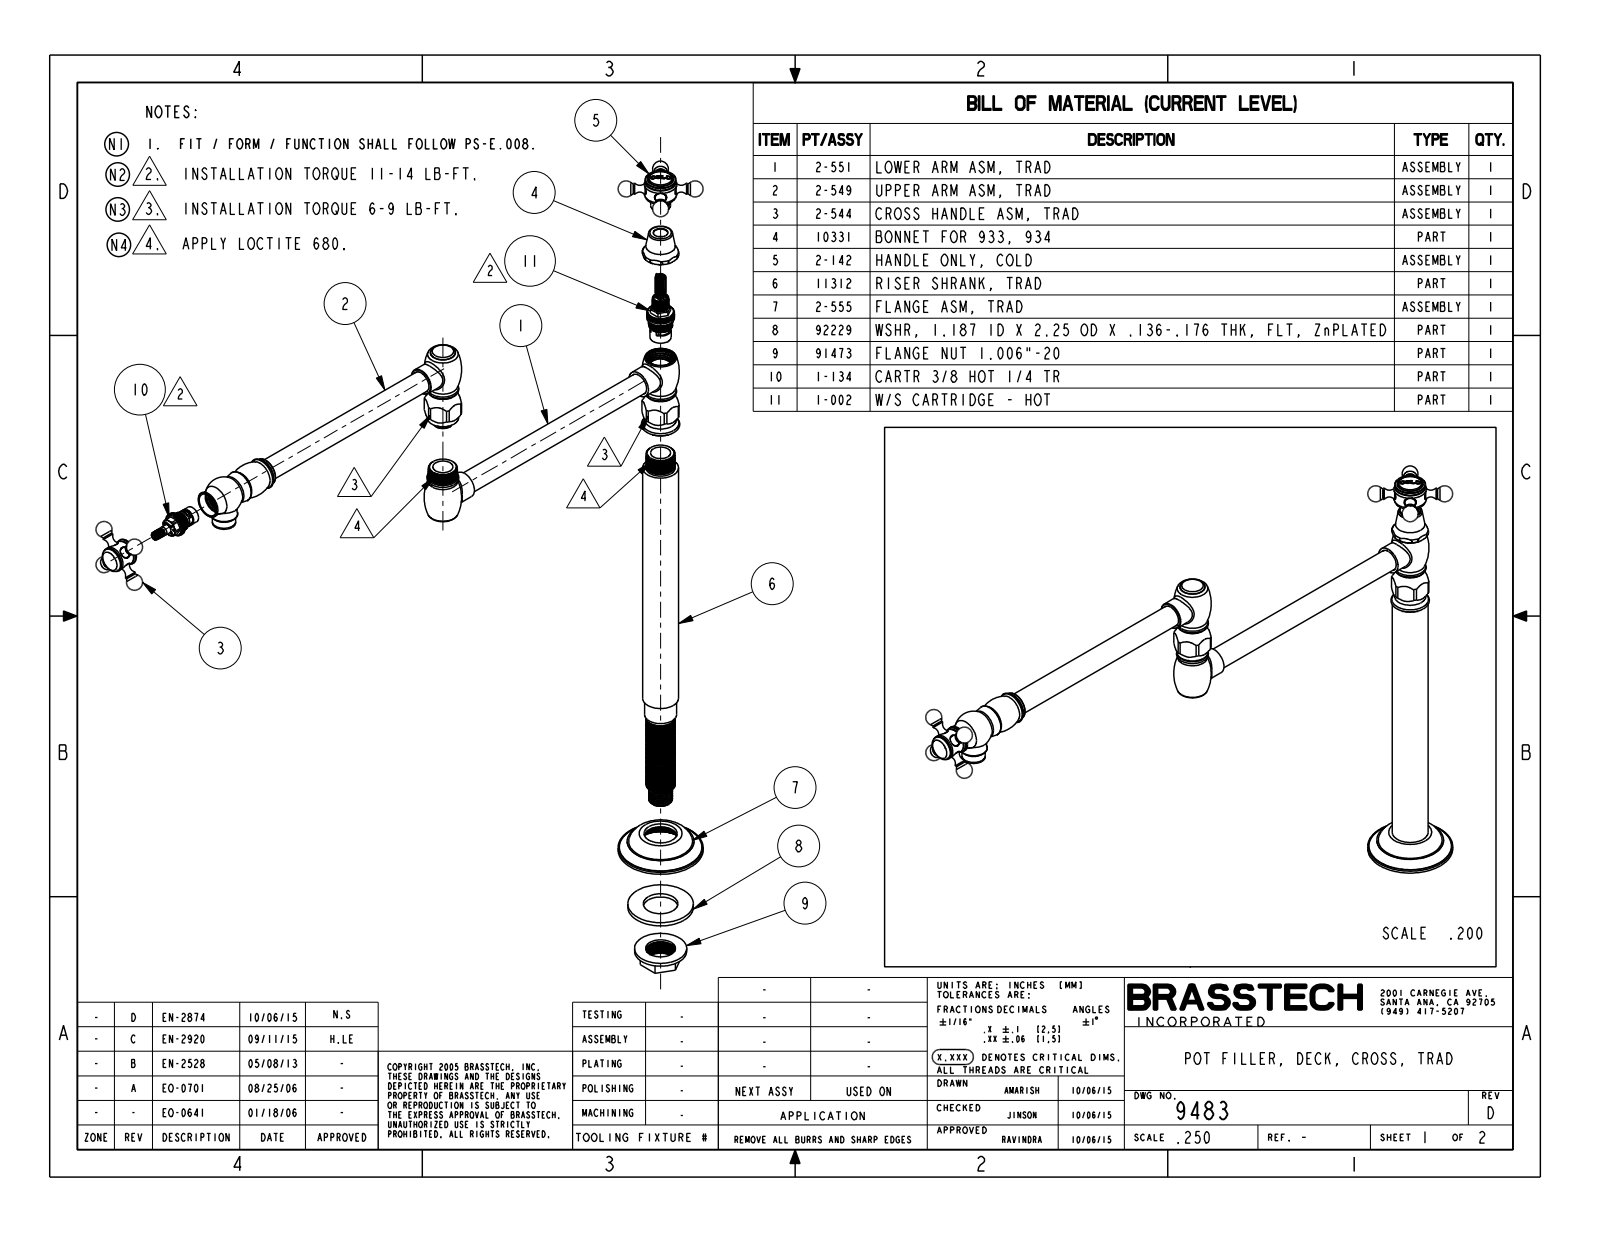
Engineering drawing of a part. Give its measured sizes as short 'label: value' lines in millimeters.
name: 11310; 91423; 11311; 91424 (+8 more)
written by: PRO/ENGINEER BY PARAMETRIC TECHNOLOGY CORPORATION, 2009300 (CONFIG_CONTROL_DESIGN)
unit: mm
bodies: 46 solids, 3513 faces (724 planar, 1374 cylindrical, 1415 other)
size: 614.5 × 513.7 × 74.2
volume: 422 300 mm³; area: 307 600 mm²
holes: 3× ⌀10.2, 3× ⌀17.5, 2× ⌀3.3, 2× ⌀5.2, 2× ⌀5.3, 2× ⌀6.7, 2× ⌀10.4, 2× ⌀12.7, 2× ⌀14.3, 2× ⌀15.7, 2× ⌀17.8, 2× ⌀19.3
bosses: 4× ⌀23.9, 4× ⌀10, 4× ⌀6.4, 4× ⌀4.6, 2× ⌀25.4, 2× ⌀23.8, 2× ⌀23.7, 2× ⌀22
rounds: 7× R1, 6× R2, 5× R0.8, 3× R0.2, 3× R1.2, 2× R0.5, 2× R1.4, 2× R1.6
face distances: 4.6, 29.7, 29.8, 17.5, 13, 388.9, 384.3, 371.3, 74.7, 12.7
hole spacings: 5.8, 30.5, 31.6, 44.1, 74.7, 75.4, 266.4, 268.4
